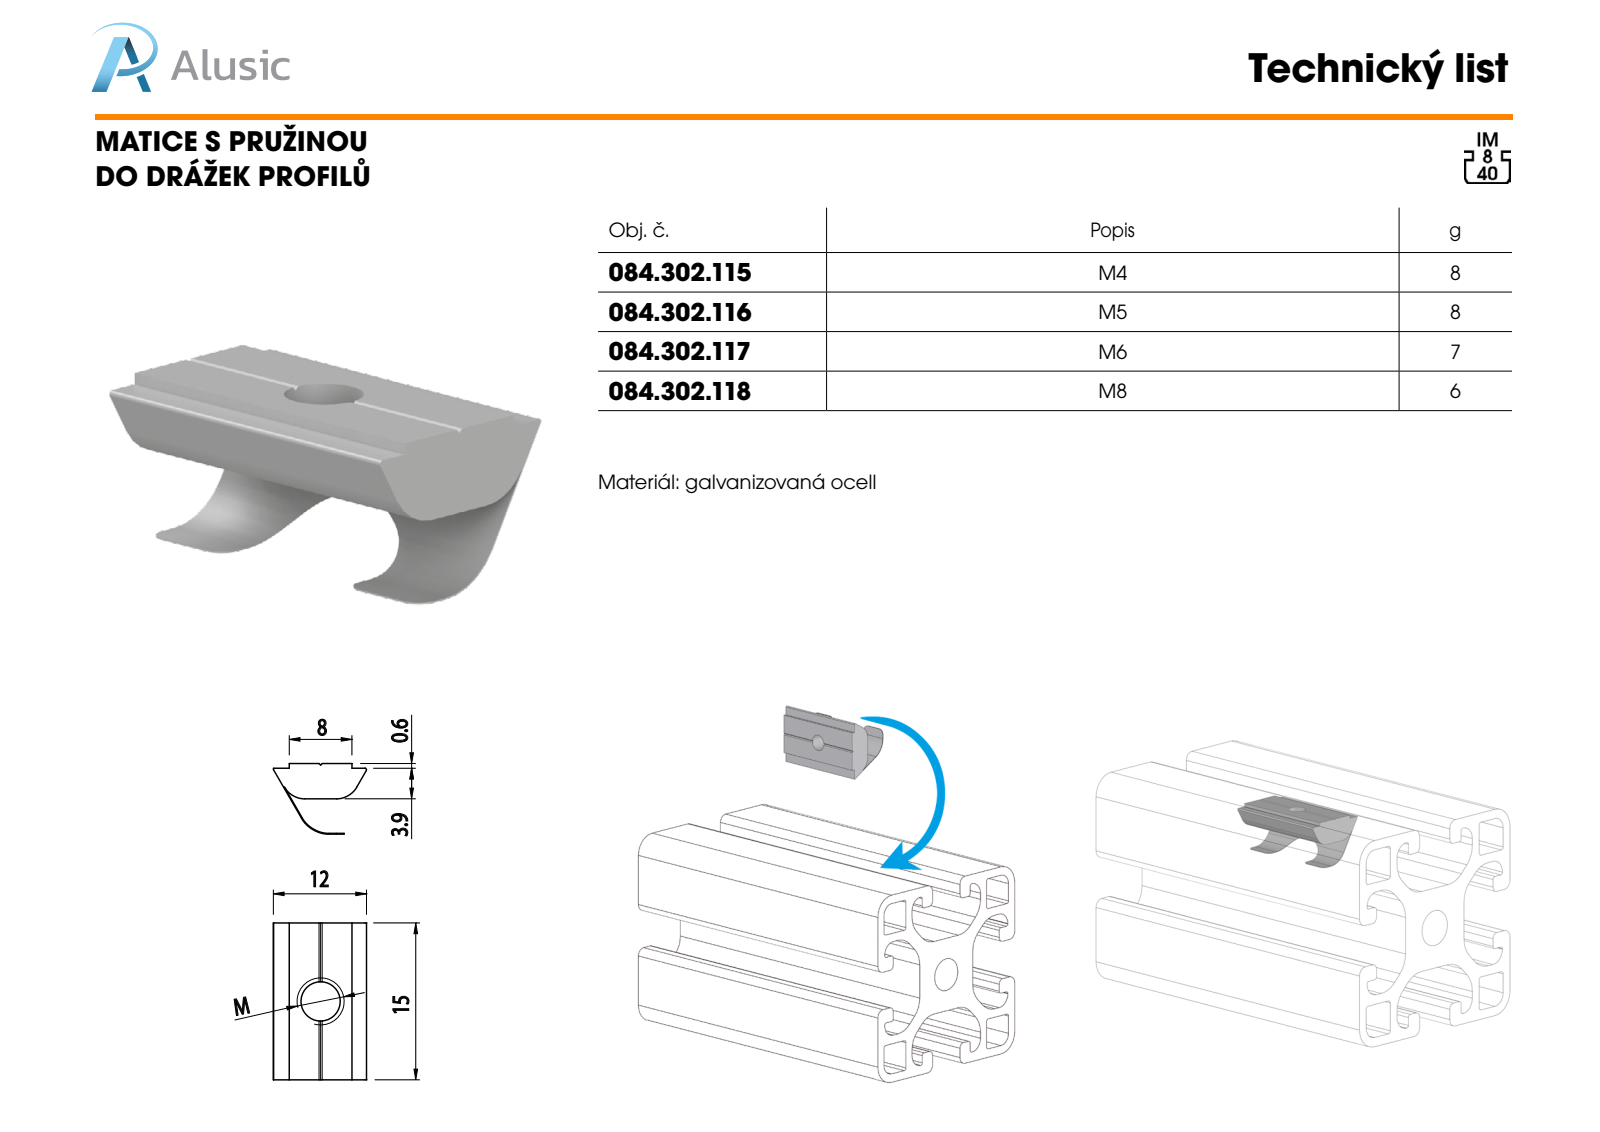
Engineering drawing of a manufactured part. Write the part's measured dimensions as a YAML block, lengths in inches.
part_name: "084.302.117"
step_written_by: "SolidWorks 2016 (CONFIG_CONTROL_DESIGN)"
units: inches
bodies: {solids: 1, faces: 41, planar: 23, cylindrical: 16, other: 2}
overall_size: [0.591, 0.463, 0.354]
volume: 0.035
surface_area: 1.16
round_holes:
  - {diameter: 0.197, count: 1}
partial_cylinders:
  - {radius: 0.008, count: 2}
  - {radius: 0.039, count: 2}
  - {radius: 0.118, count: 2}
  - {radius: 0.079, count: 1}
  - {radius: 0.154, count: 1}
  - {radius: 0.157, count: 1}
  - {radius: 0.169, count: 1}
face_to_face_distances: [0.177, 0.024, 0.154, 0.591, 0.173, 0.327, 0.35, 0.331, 0.354, 0.315]
